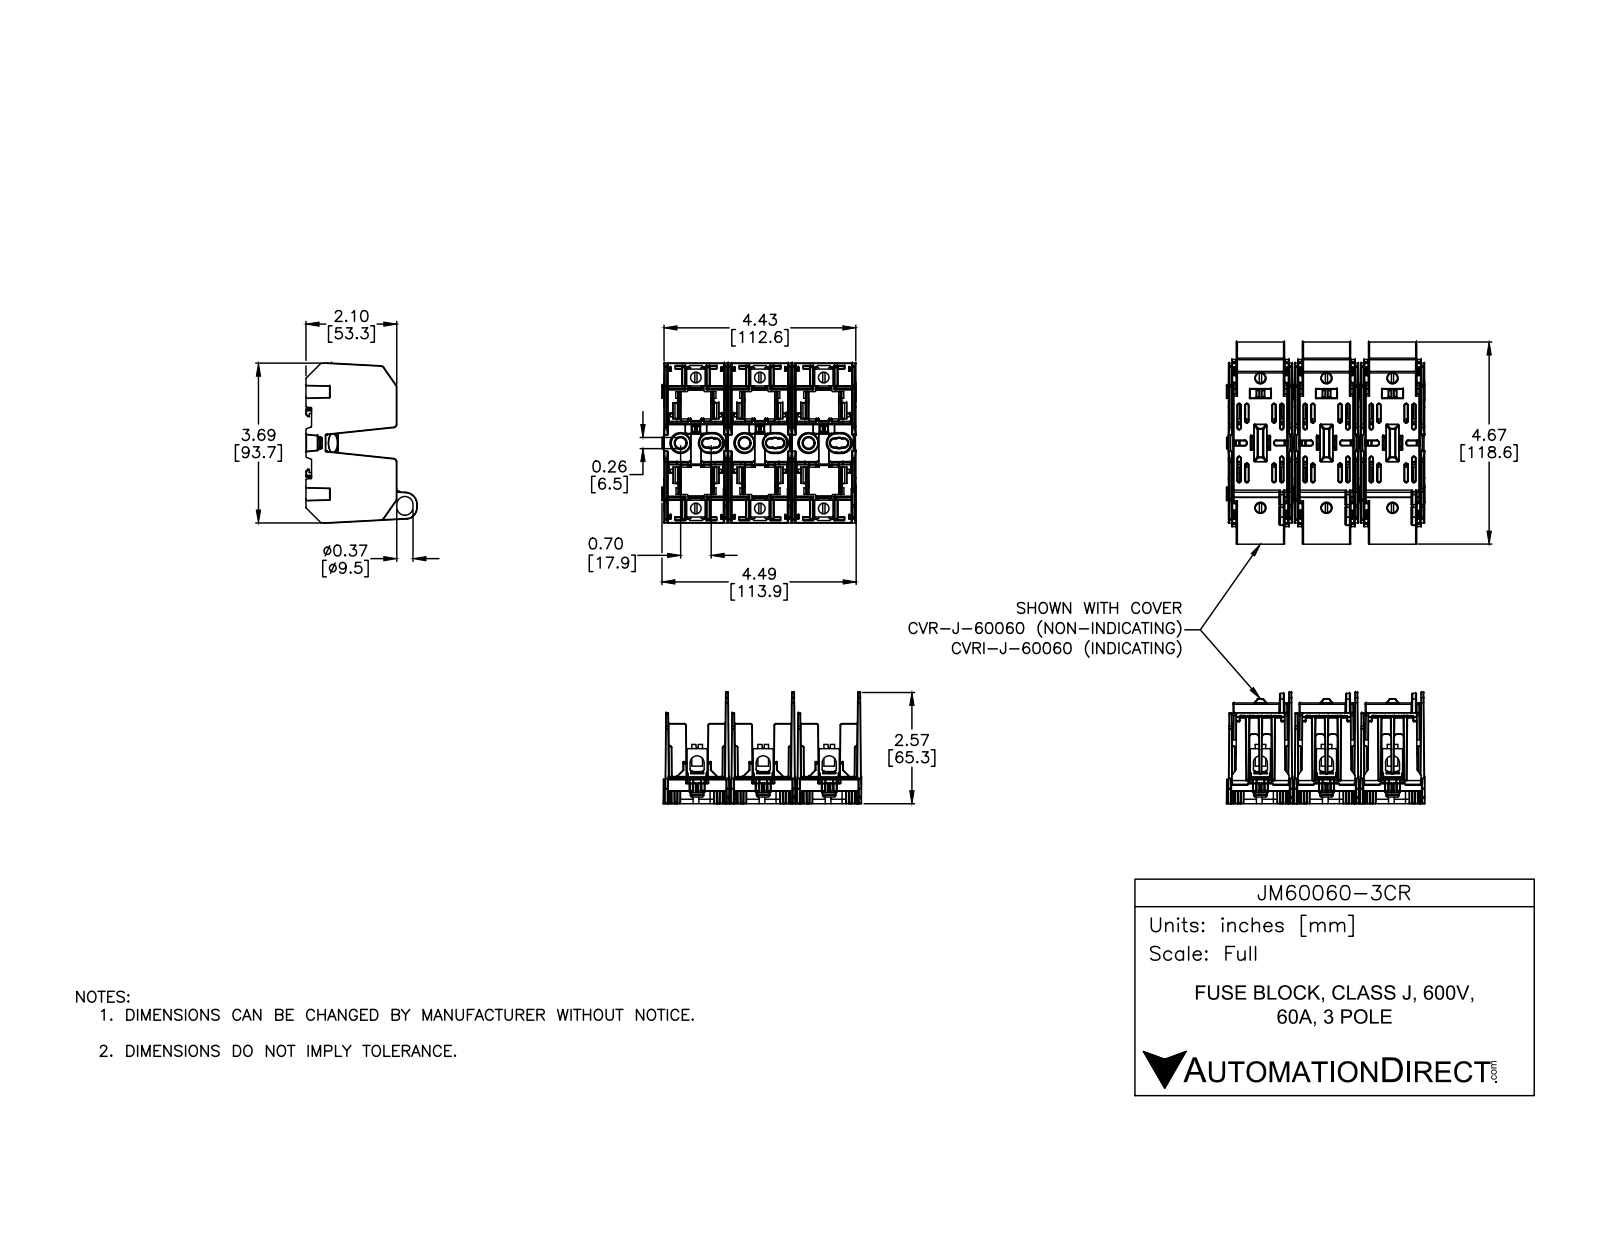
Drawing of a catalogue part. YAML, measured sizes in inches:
part_name: "JM60060-1CR; JM60060-3CR"
step_written_by: "SolidWorks 2016 (AUTOMOTIVE_DESIGN)"
units: inches
bodies: {solids: 24, faces: 1152, planar: 630, cylindrical: 522, other: 0}
overall_size: [4.03, 3.577, 1.158]
volume: 1.064
surface_area: 54.9
round_holes:
  - {diameter: 0.225, count: 6}
  - {diameter: 0.244, count: 6}
round_bosses_or_shafts:
  - {diameter: 0.05, count: 24}
  - {diameter: 0.244, count: 6}
partial_cylinders:
  - {radius: 0.012, count: 52}
  - {radius: 0.039, count: 48}
  - {radius: 0.02, count: 24}
  - {radius: 0.079, count: 24}
  - {radius: 0.031, count: 12}
  - {radius: 0.05, count: 12}
  - {radius: 0.051, count: 12}
  - {radius: 0.063, count: 12}
face_to_face_distances: [0.032, 0.028, 1.48, 0.06, 1.448, 1.484, 2.961, 1.512, 1.476, 0.036]
hole_center_spacings: [1.483, 1.483, 2.967, 0.676, 0.676, 1.628, 1.632, 1.676]
